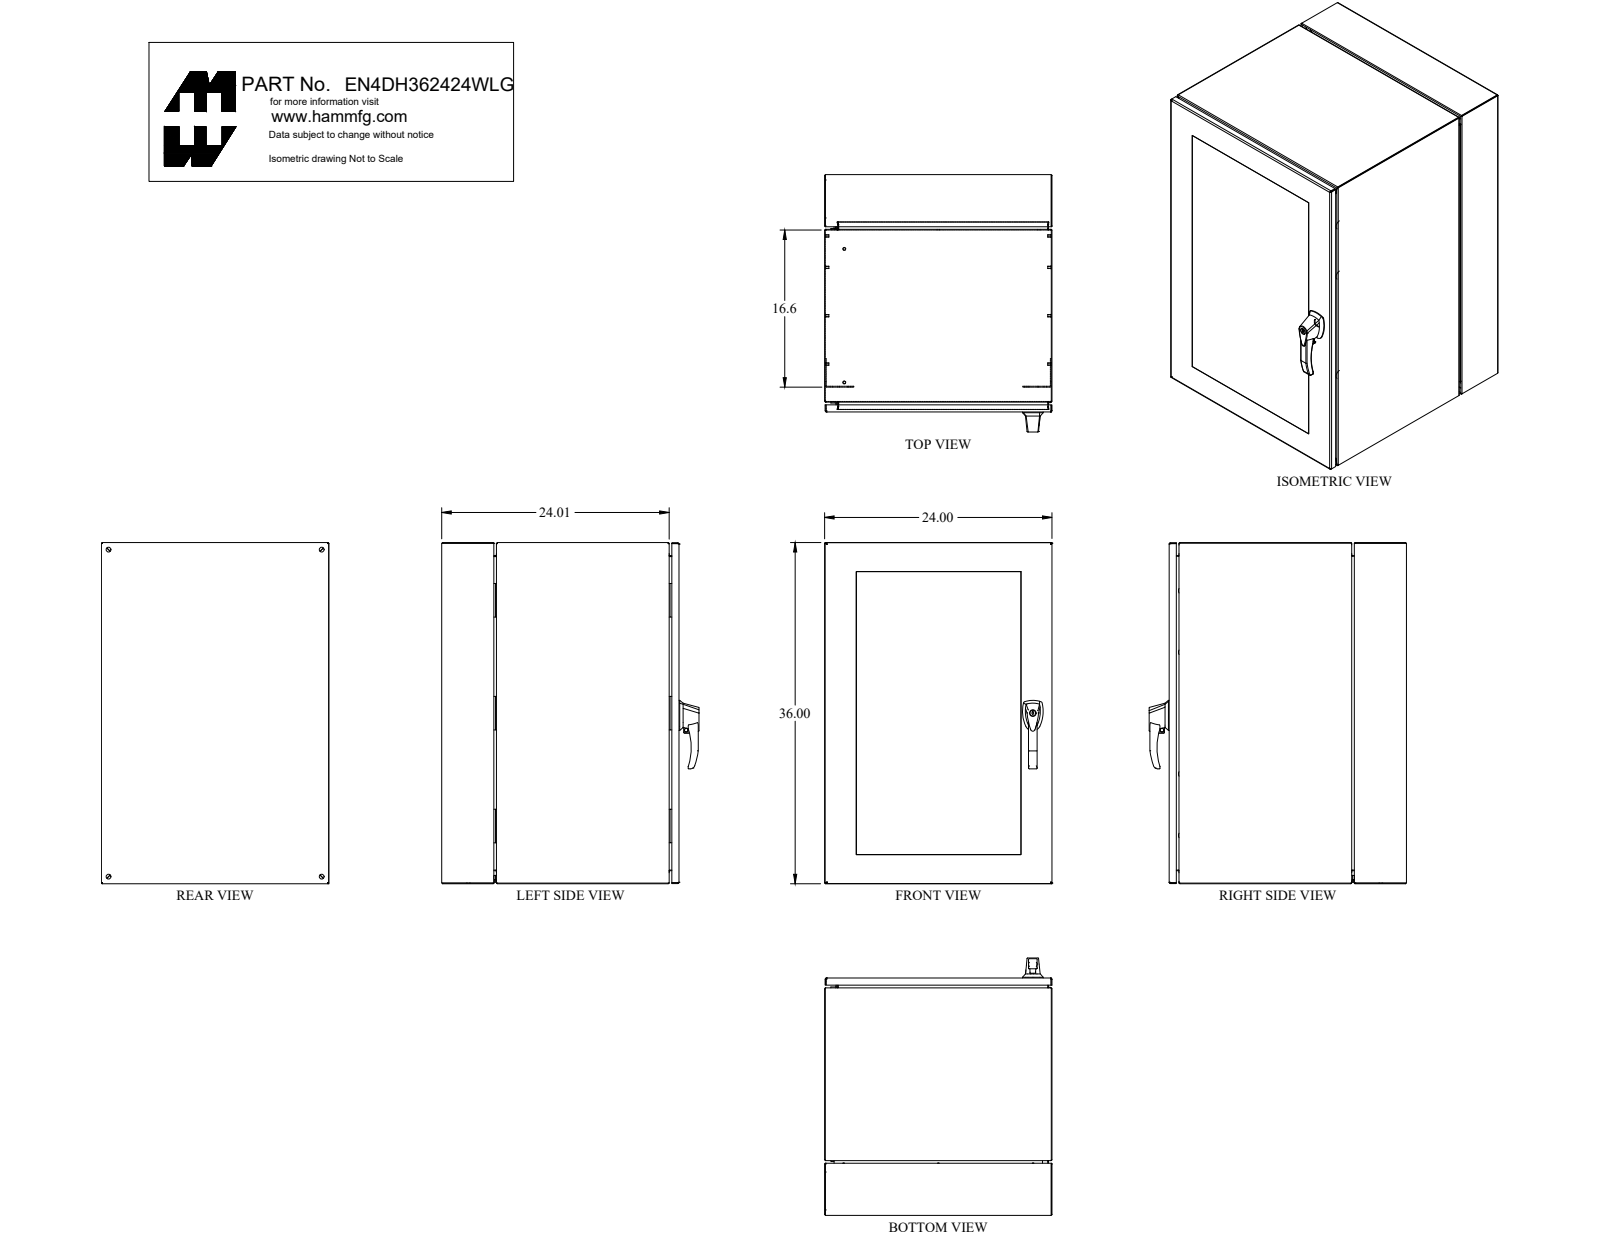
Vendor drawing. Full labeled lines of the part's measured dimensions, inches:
Part name (STEP PRODUCT): EN4DH362424WLG
STEP written by: SolidWorks 2019 (CONFIG_CONTROL_DESIGN)
Units: inches
Bodies: 283 solids, 5306 faces (2893 planar, 1375 cylindrical, 1038 other)
Overall size (bounding box): 36 × 27.158 × 24.001
Volume: 609.1 in³ · Surface area: 13 040 in²
Round holes (diameter × count): ⌀0.177 ×114, ⌀0.25 ×43, ⌀0.125 ×36, ⌀0.13 ×22, ⌀0.196 ×19, ⌀0.188 ×14, ⌀0.194 ×14, ⌀0.237 ×14, ⌀0.257 ×9, ⌀0.275 ×9, ⌀0.281 ×9, ⌀0.173 ×8
Round bosses / shafts (diameter × count): ⌀0.25 ×30, ⌀0.313 ×26, ⌀0.368 ×22, ⌀0.226 ×20, ⌀0.164 ×20, ⌀0.236 ×16, ⌀0.472 ×14, ⌀0.433 ×14
Partial cylindrical surfaces — rounded edges, fillets, slot ends (radius × count): R0.125 ×37, R0.036 ×33, R0.108 ×33, R0.25 ×26, R0.06 ×24, R0.122 ×20, R0.5 ×17, R0.079 ×16
Main face-to-face distances: 0.072, 23.928, 35.928, 23.856, 0.095, 24.971, 25.043, 24, 35.856, 36
Hole centre spacings: 0.985, 11.906, 11.907, 15.25, 20.382, 9.125, 10.922, 11.906
